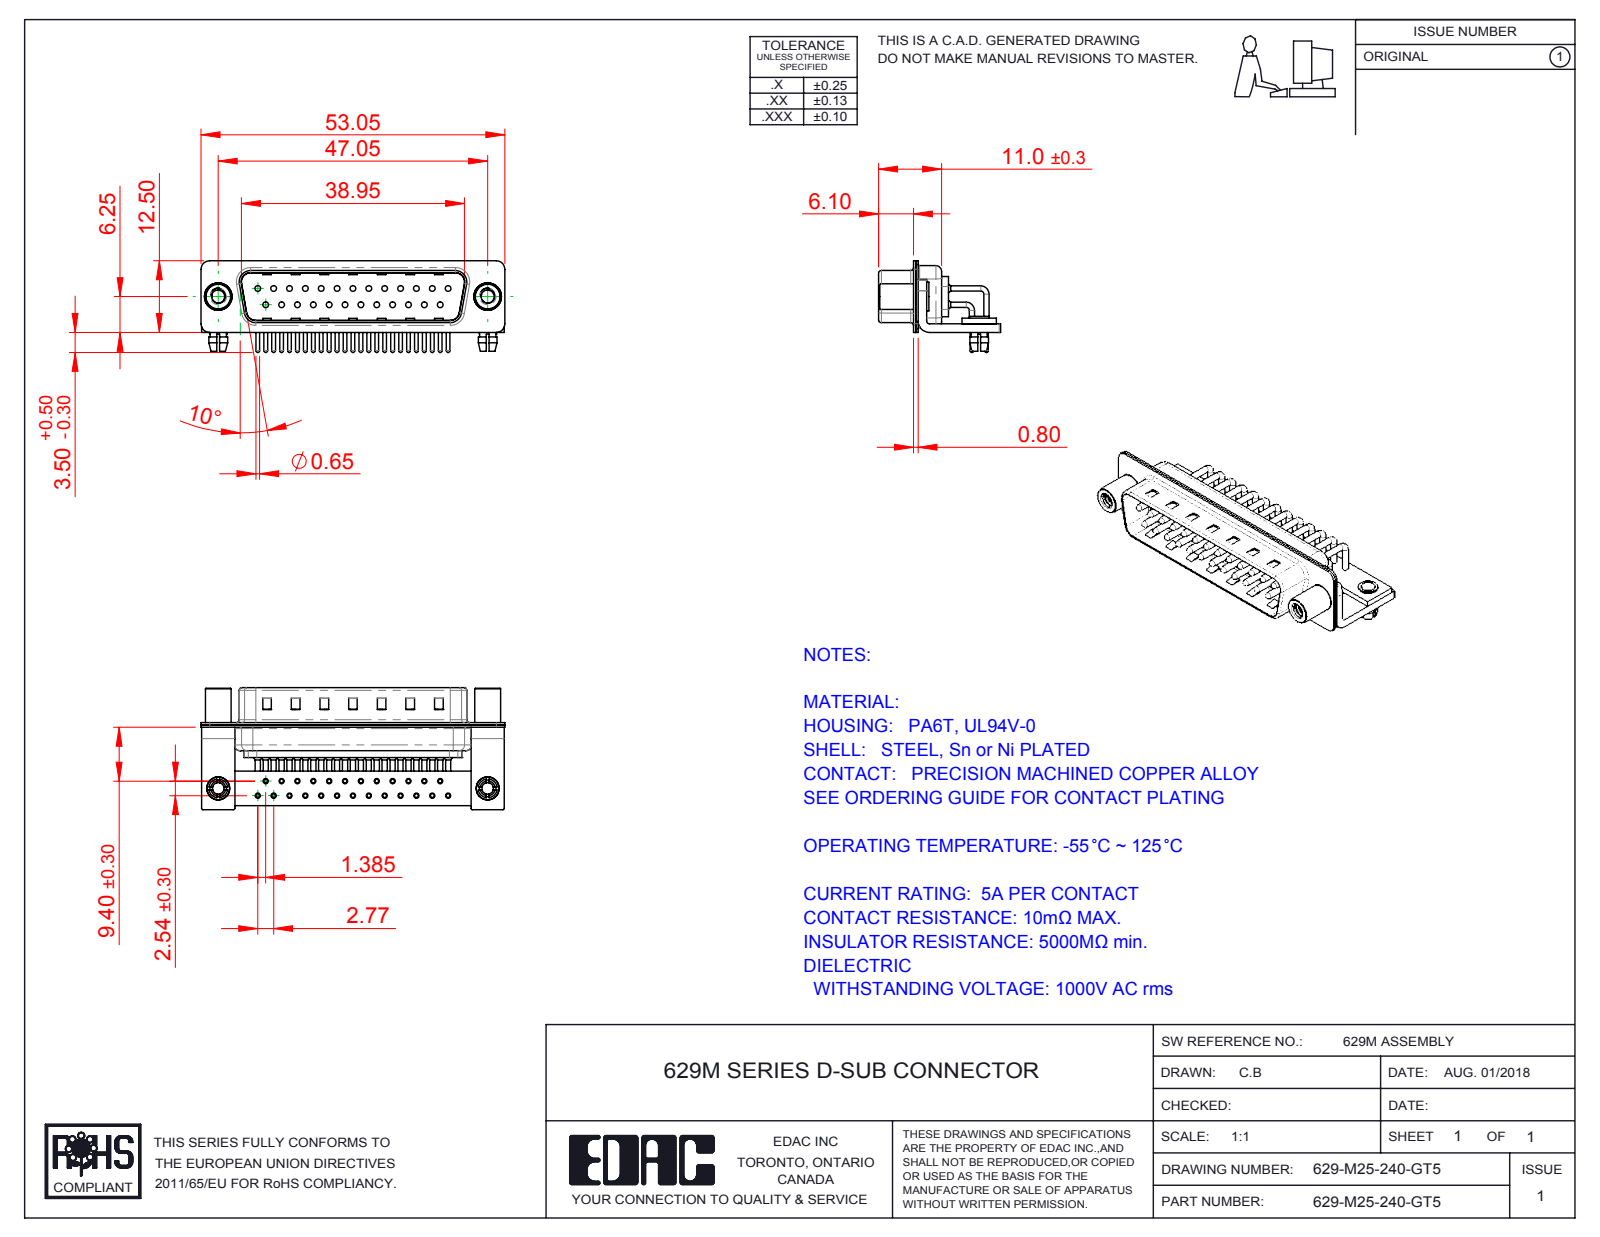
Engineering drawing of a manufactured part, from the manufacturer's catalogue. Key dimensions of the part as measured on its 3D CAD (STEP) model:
Part name (STEP PRODUCT): 629M Contact Row 1; 629M Contact Row 2; 629-M25-240-GT5; 629M 4-40 Threaded Standoff (+6 more)
STEP written by: SolidWorks 2016 (CONFIG_CONTROL_DESIGN)
Units: millimetres
Bodies: 35 solids, 3368 faces (1847 planar, 1183 cylindrical, 338 other)
Overall size (bounding box): 53.05 × 21.3 × 16
Volume: 3 638 mm³ · Surface area: 9 694 mm²
Round holes (diameter × count): ⌀2 ×27, ⌀0.9 ×25, ⌀1 ×25, ⌀1.7 ×25, ⌀2.26 ×2, ⌀2.5 ×2, ⌀3.2 ×2, ⌀4 ×2, ⌀4.8 ×2
Round bosses / shafts (diameter × count): ⌀1.5 ×25, ⌀0.9 ×25, ⌀0.65 ×25, ⌀5 ×2, ⌀4.9 ×2, ⌀4.5 ×2, ⌀4 ×2, ⌀3.4 ×2
Partial cylindrical surfaces — rounded edges, fillets, slot ends (radius × count): R1.01 ×25, R0.25 ×16, R1.5 ×16, R2 ×13, R0.5 ×9, R1.6 ×8, R0.6 ×4, R0.65 ×4
Main face-to-face distances: 0.4, 0.85, 1.25, 1.5, 9.55, 10.4, 0.8, 8.3, 1, 1.9
Hole centre spacings: 2.77, 5.54, 8.31, 11.08, 13.85, 3.16, 4.87, 16.62
